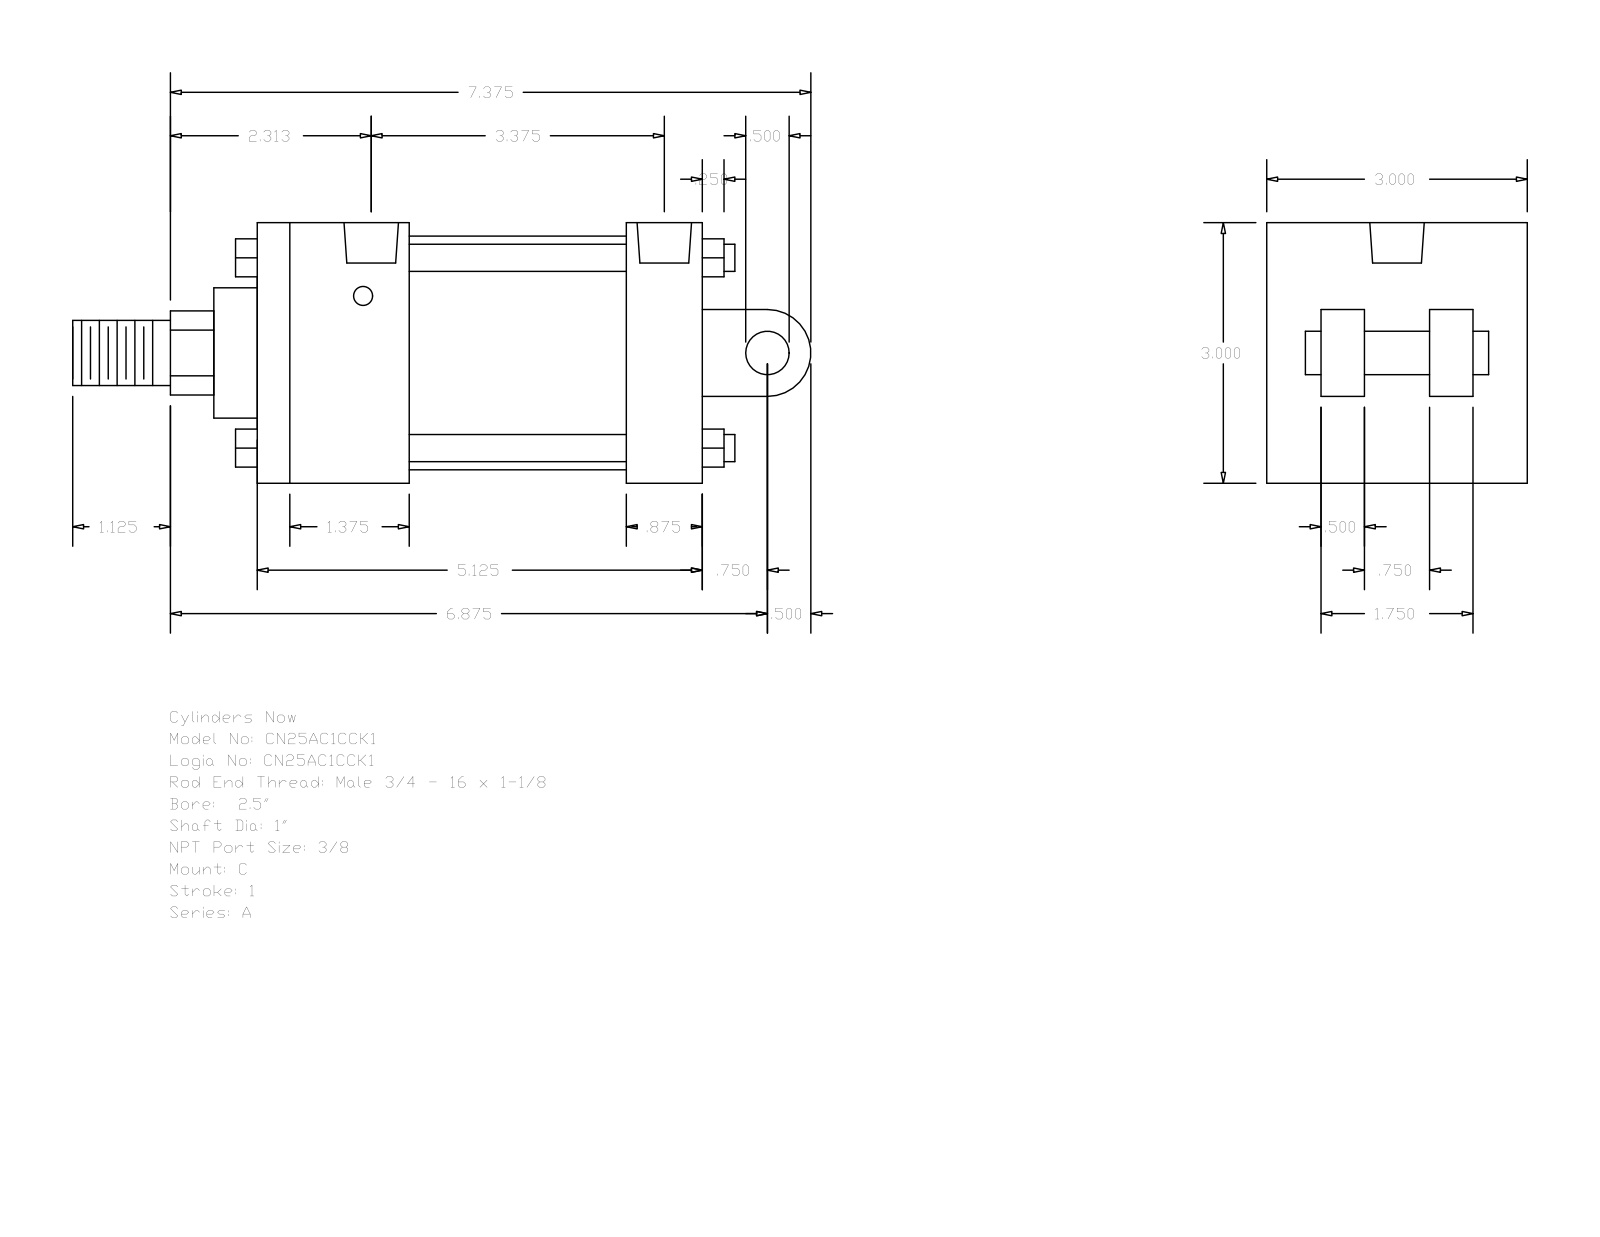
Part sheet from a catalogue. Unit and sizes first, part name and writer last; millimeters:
Units: millimetres
Overall size (bounding box): 215.9 × 76.2 × 76.2
Round holes (diameter × count): ⌀5.56 ×4, ⌀15.93 ×2
Round bosses / shafts (diameter × count): ⌀7.94 ×4, ⌀68.33 ×1, ⌀38.1 ×1, ⌀25.4 ×1, ⌀19.05 ×1, ⌀12.7 ×1
Partial cylindrical surfaces — rounded edges, fillets, slot ends (radius × count): R12.29 ×1, R12.7 ×1
Main face-to-face distances: 76.2, 130.17, 12.7, 63.5, 44.45, 107.95, 85.72, 22.22, 15.87, 25.4
Hole centre spacings: 2.38, 88.1, 90.48, 85.72
Bodies: 0 solids, 135 faces (102 planar, 33 cylindrical, 0 other)
Part name (STEP PRODUCT): A_C__0250_1
STEP written by: GSSL Pune (CONFIG_CONTROL_DESIGN)
